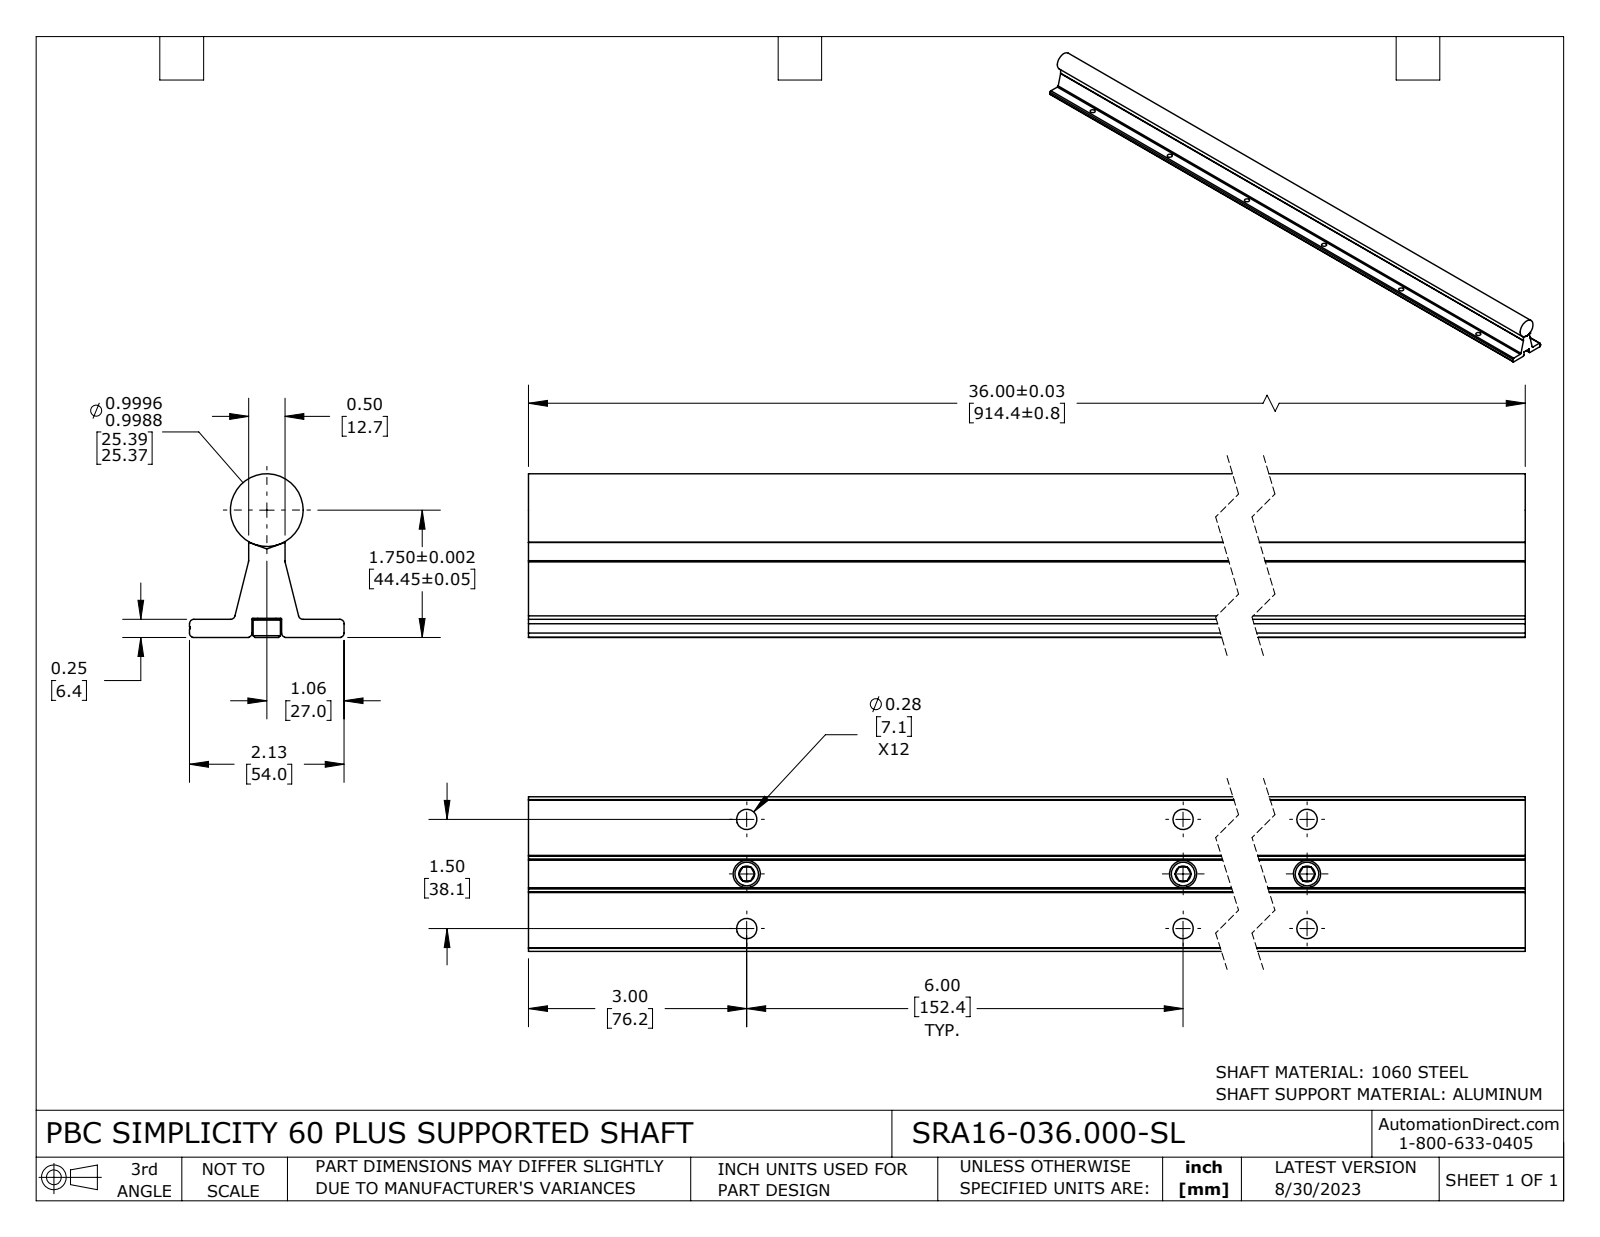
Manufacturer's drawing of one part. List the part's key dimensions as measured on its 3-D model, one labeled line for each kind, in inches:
Part name (STEP PRODUCT): SRA16-036.000-SL
STEP written by: SolidWorks 2021 (CONFIG_CONTROL_DESIGN)
Units: inches
Bodies: 8 solids, 283 faces (93 planar, 100 cylindrical, 90 other)
Overall size (bounding box): 36 × 2.25 × 2.125
Volume: 67.13 in³ · Surface area: 384.3 in²
Round holes (diameter × count): ⌀0.281 ×18, ⌀0.213 ×6, ⌀0.313 ×6
Round bosses / shafts (diameter × count): ⌀0.375 ×6, ⌀0.25 ×6, ⌀1 ×1
Partial cylindrical surfaces — rounded edges, fillets, slot ends (radius × count): R0.06 ×6, R0.063 ×4, R0.015 ×2, R0.032 ×2
Main face-to-face distances: 0.25, 0.045, 0.455, 0.265, 0.015, 0.5, 0.813, 0.857, 1.268, 1.313
Hole centre spacings: 6.047, 12.023, 6, 0.75, 12, 18.016, 6.185, 18
